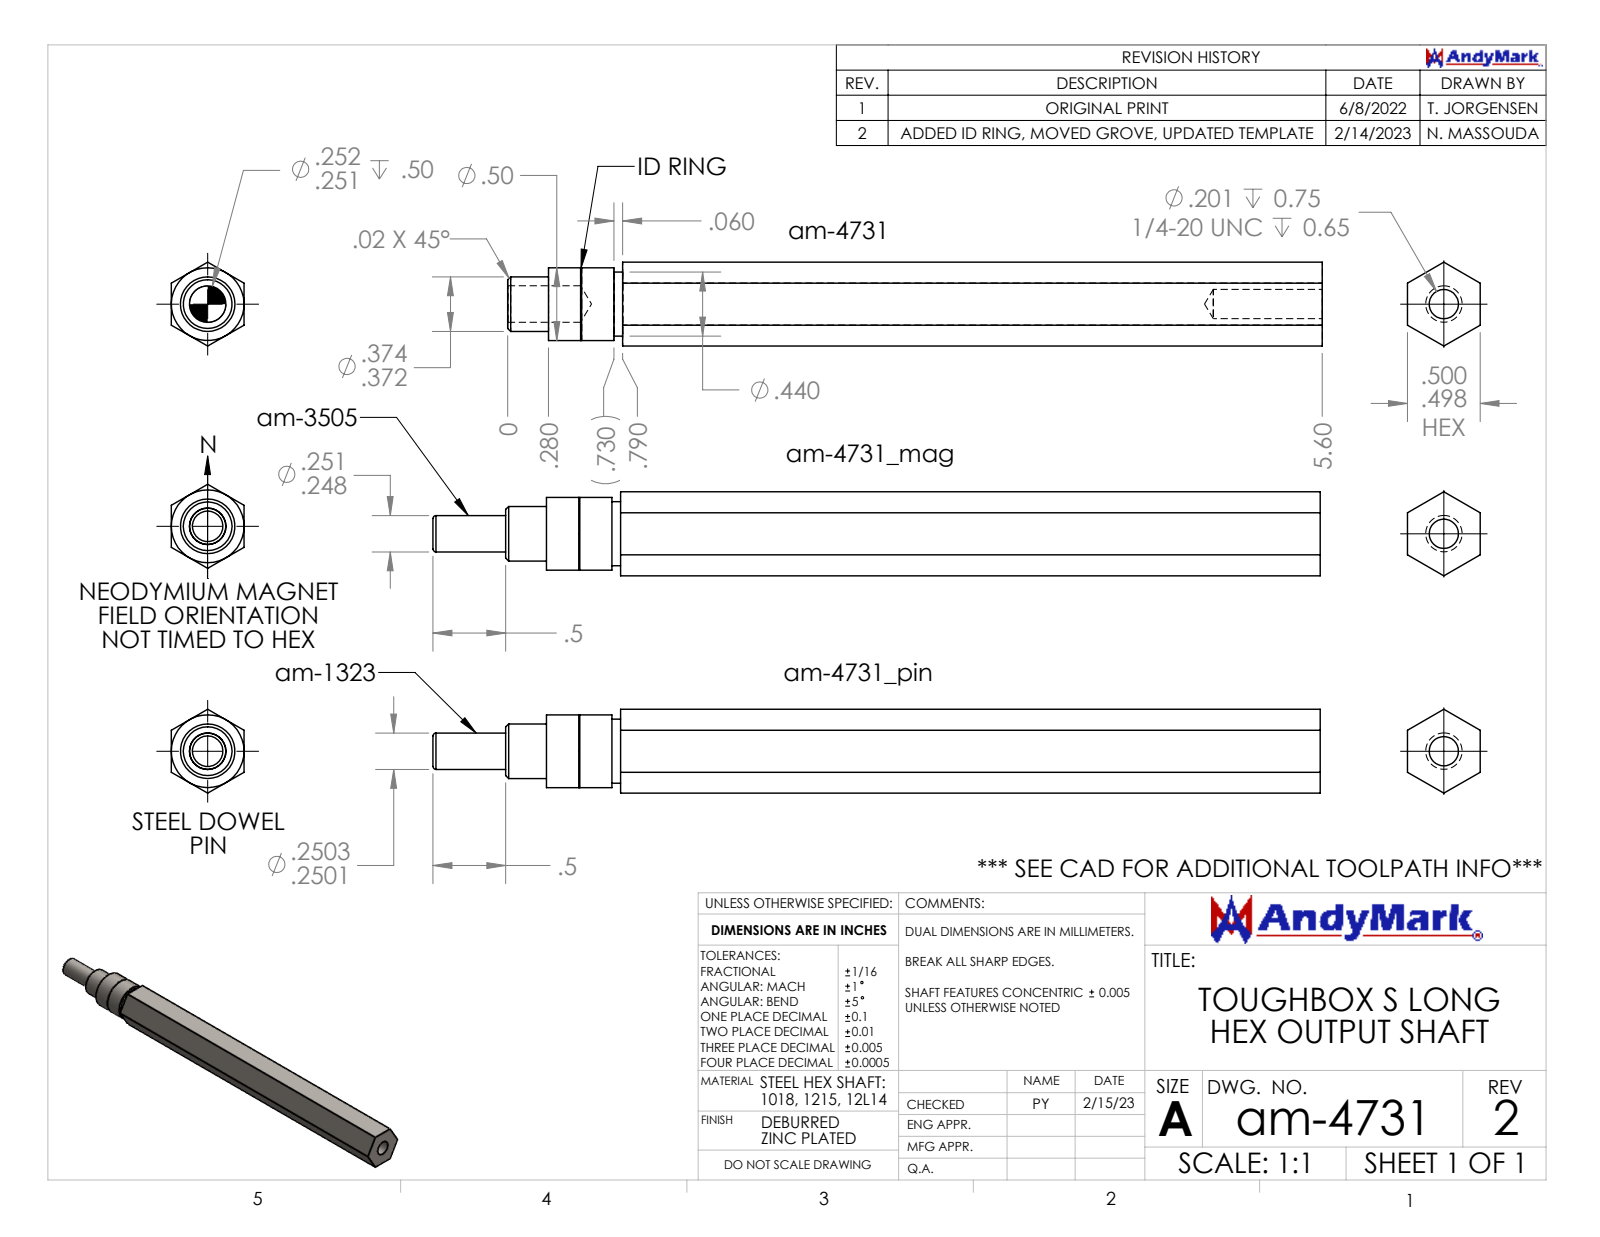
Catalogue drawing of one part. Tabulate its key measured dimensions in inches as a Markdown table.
| quantity | value |
| --- | --- |
| part name | am-4731 ToughBox S Long Hex Output Shaft |
| STEP written by | SolidWorks 2022 (CONFIG_CONTROL_DESIGN) |
| units | inches |
| bodies | 1 solid, 33 faces (11 planar, 12 cylindrical, 10 other) |
| overall size | 5.6 × 0.577 × 0.5 |
| volume | 1.119 in³ |
| surface area | 10.85 in² |
| round holes (diameter × count) | 0.201 × 1, 0.251 × 1 |
| round bosses / shafts (diameter × count) | 0.5 × 1, 0.44 × 1, 0.375 × 1 |
| main face-to-face distances | 0.5, 5.32, 0.51, 4.81, 0.45, 0.06, 4.87, 0.28, 0.73, 0.79 |
